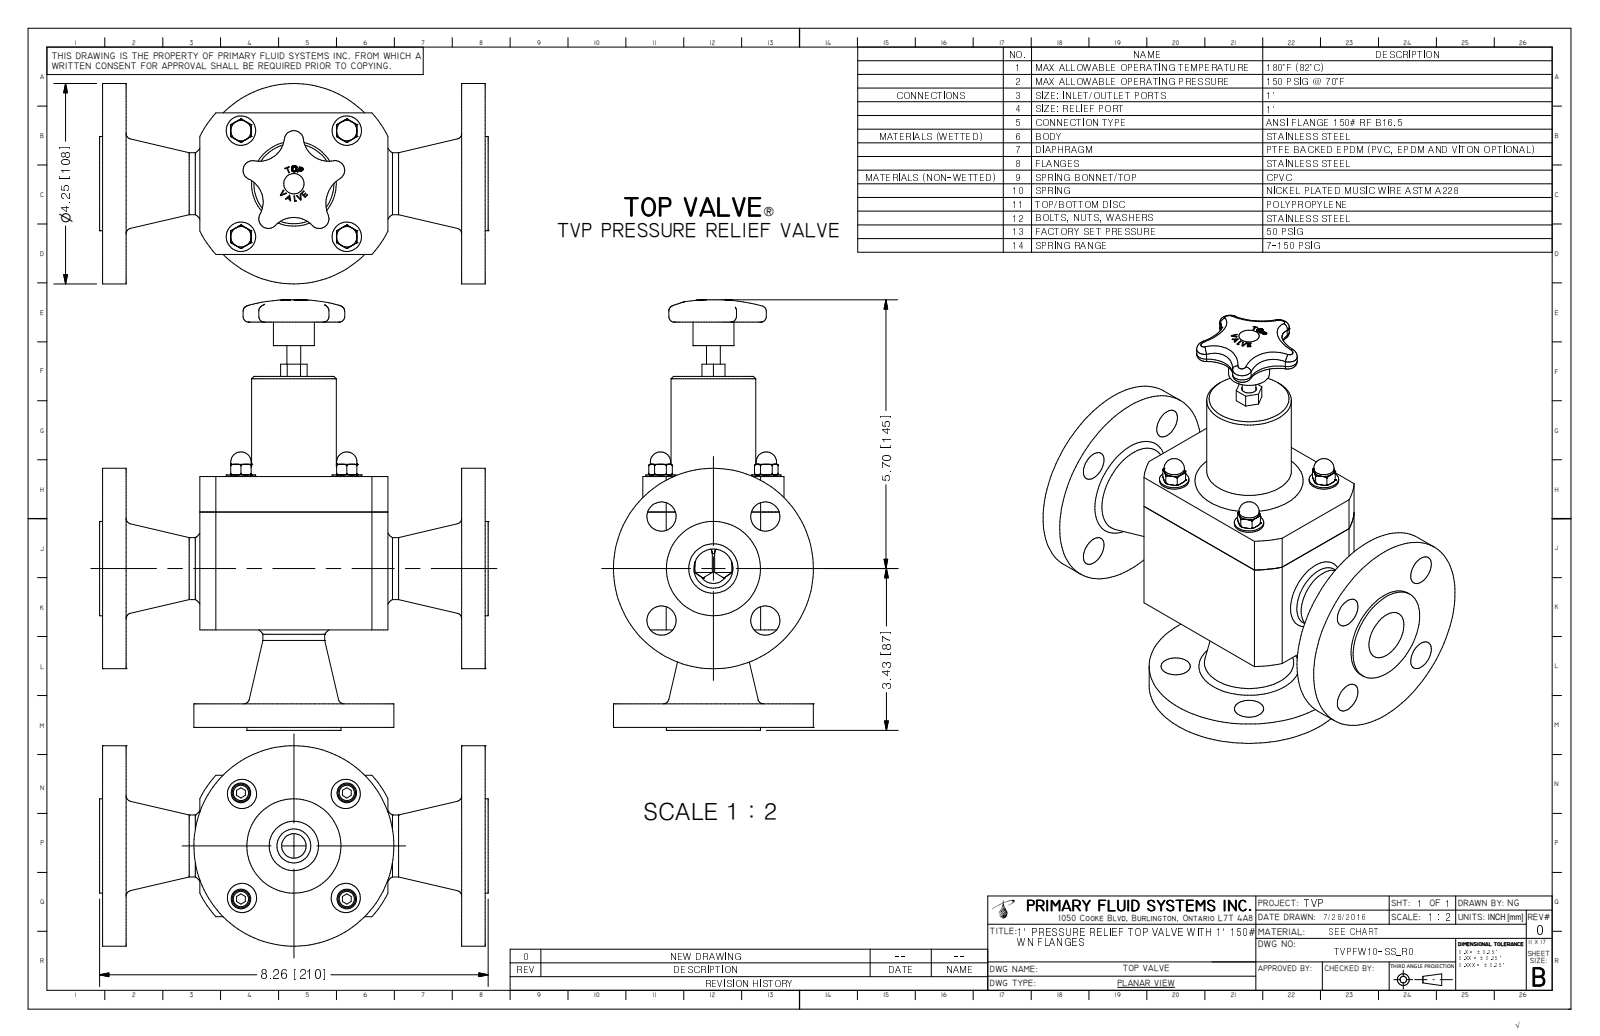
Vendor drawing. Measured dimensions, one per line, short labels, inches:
name: TVPFW10-SS_R0
written by: Autodesk Inventor 2009 (AUTOMOTIVE_DESIGN)
unit: in
bodies: 1 solid, 380 faces (156 planar, 69 cylindrical, 155 other)
size: 9.13 × 8.26 × 4.25
volume: 68.81 in³; area: 237.3 in²
holes: 8× ⌀0.62, 4× ⌀0.175, 2× ⌀1.049, 1× ⌀2.525
bosses: 4× ⌀0.625, 4× ⌀0.433, 4× ⌀0.375, 2× ⌀4.25, 2× ⌀2, 2× ⌀1.315, 1× ⌀2.5, 1× ⌀1.8
rounds: 5× R0.085, 5× R0.205, 4× R0.536, 4× R0.656, 1× R0.625, 1× R0.745, 1× R2.238
face distances: 0.5, 2.067, 1.567, 7.635, 3, 8.135, 6.067, 5.567, 7.135, 0.063
hole spacings: 1.56, 2.206, 2.228, 2.228, 2.25, 3.12, 0.031, 3.151
